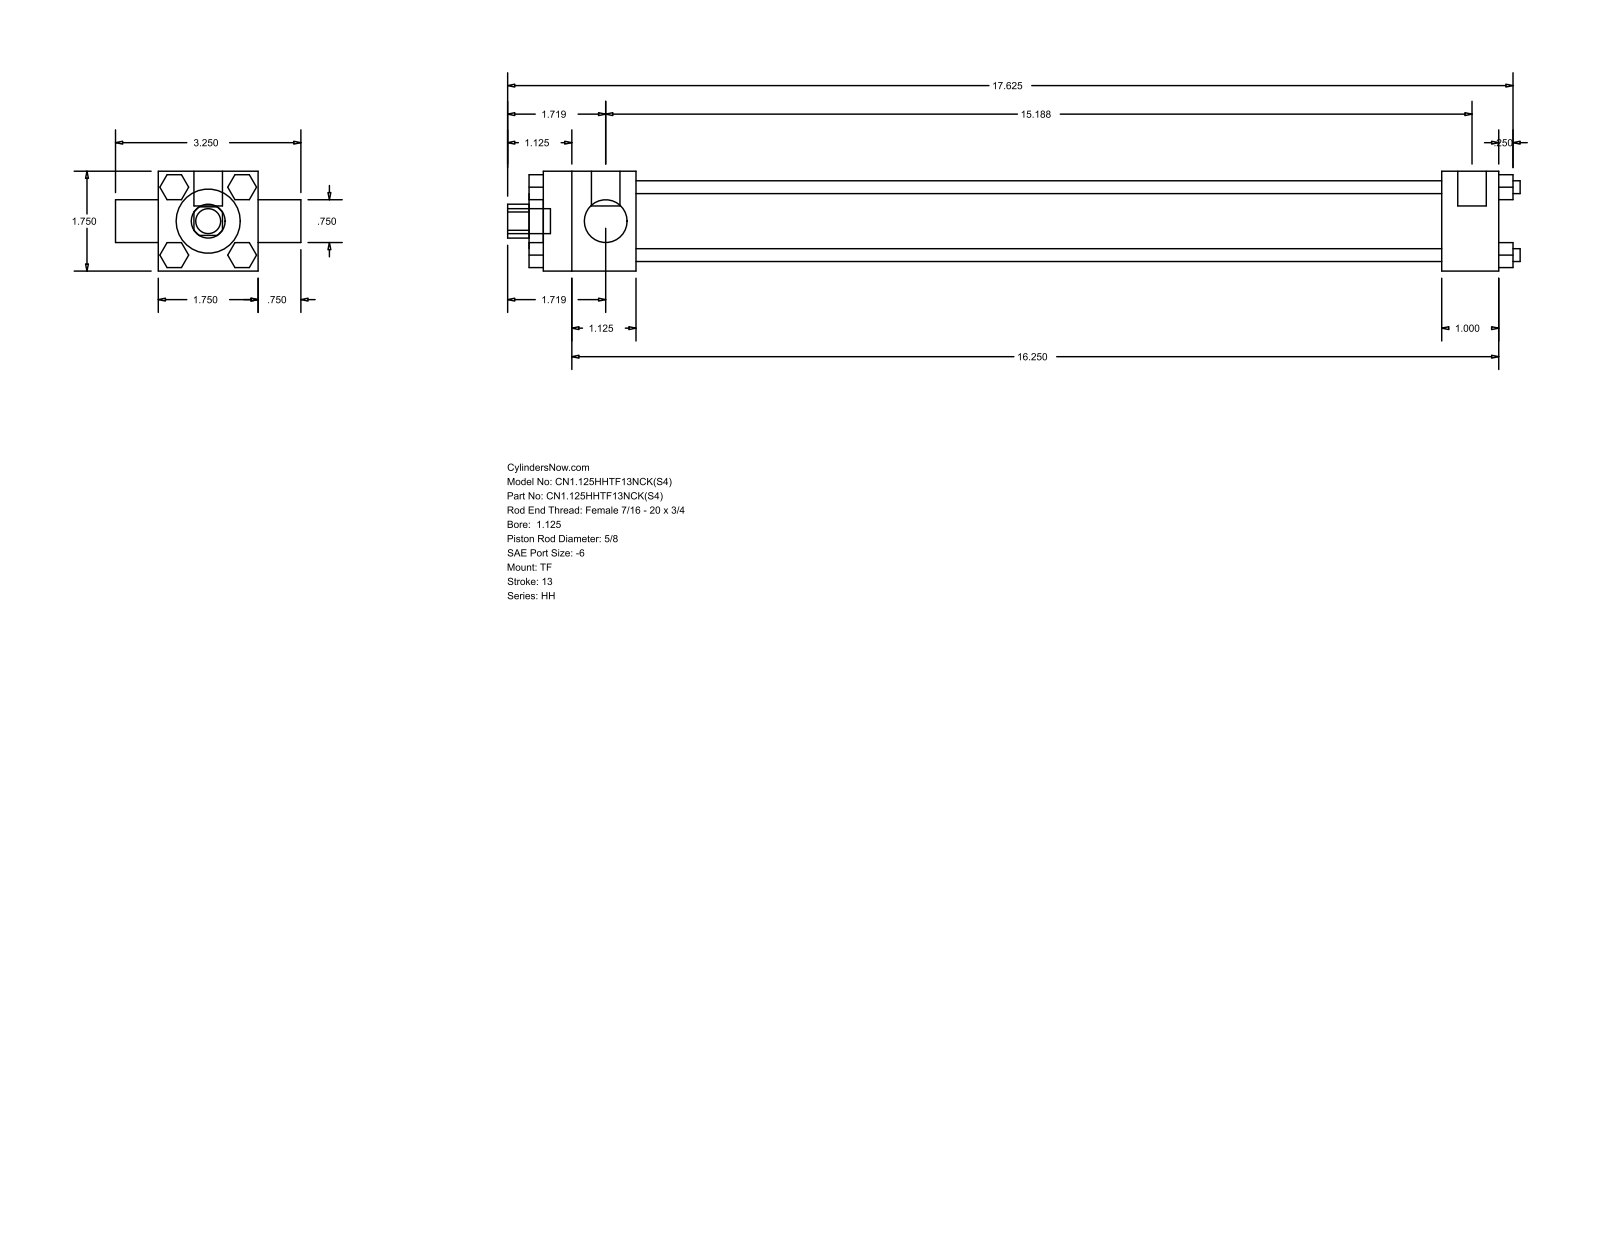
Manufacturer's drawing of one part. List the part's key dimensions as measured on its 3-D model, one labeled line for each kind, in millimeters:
Part name (STEP PRODUCT): HH_TF__0112_0.625
STEP written by: GSSL Pune (CONFIG_CONTROL_DESIGN)
Units: millimetres
Bodies: 0 solids, 120 faces (92 planar, 28 cylindrical, 0 other)
Overall size (bounding box): 450.85 × 82.55 × 44.45
Round holes (diameter × count): ⌀15.88 ×1, ⌀19.05 ×1, ⌀28.57 ×1, ⌀34.92 ×1
Round bosses / shafts (diameter × count): ⌀5.71 ×4, ⌀5.56 ×3, ⌀12.7 ×2, ⌀11.11 ×1
Partial cylindrical surfaces — rounded edges, fillets, slot ends (radius × count): R7.54 ×1
Main face-to-face distances: 44.46, 11.11, 358.78, 384.17, 25.39, 41.27, 400.05, 425.44, 47.62, 6.35
